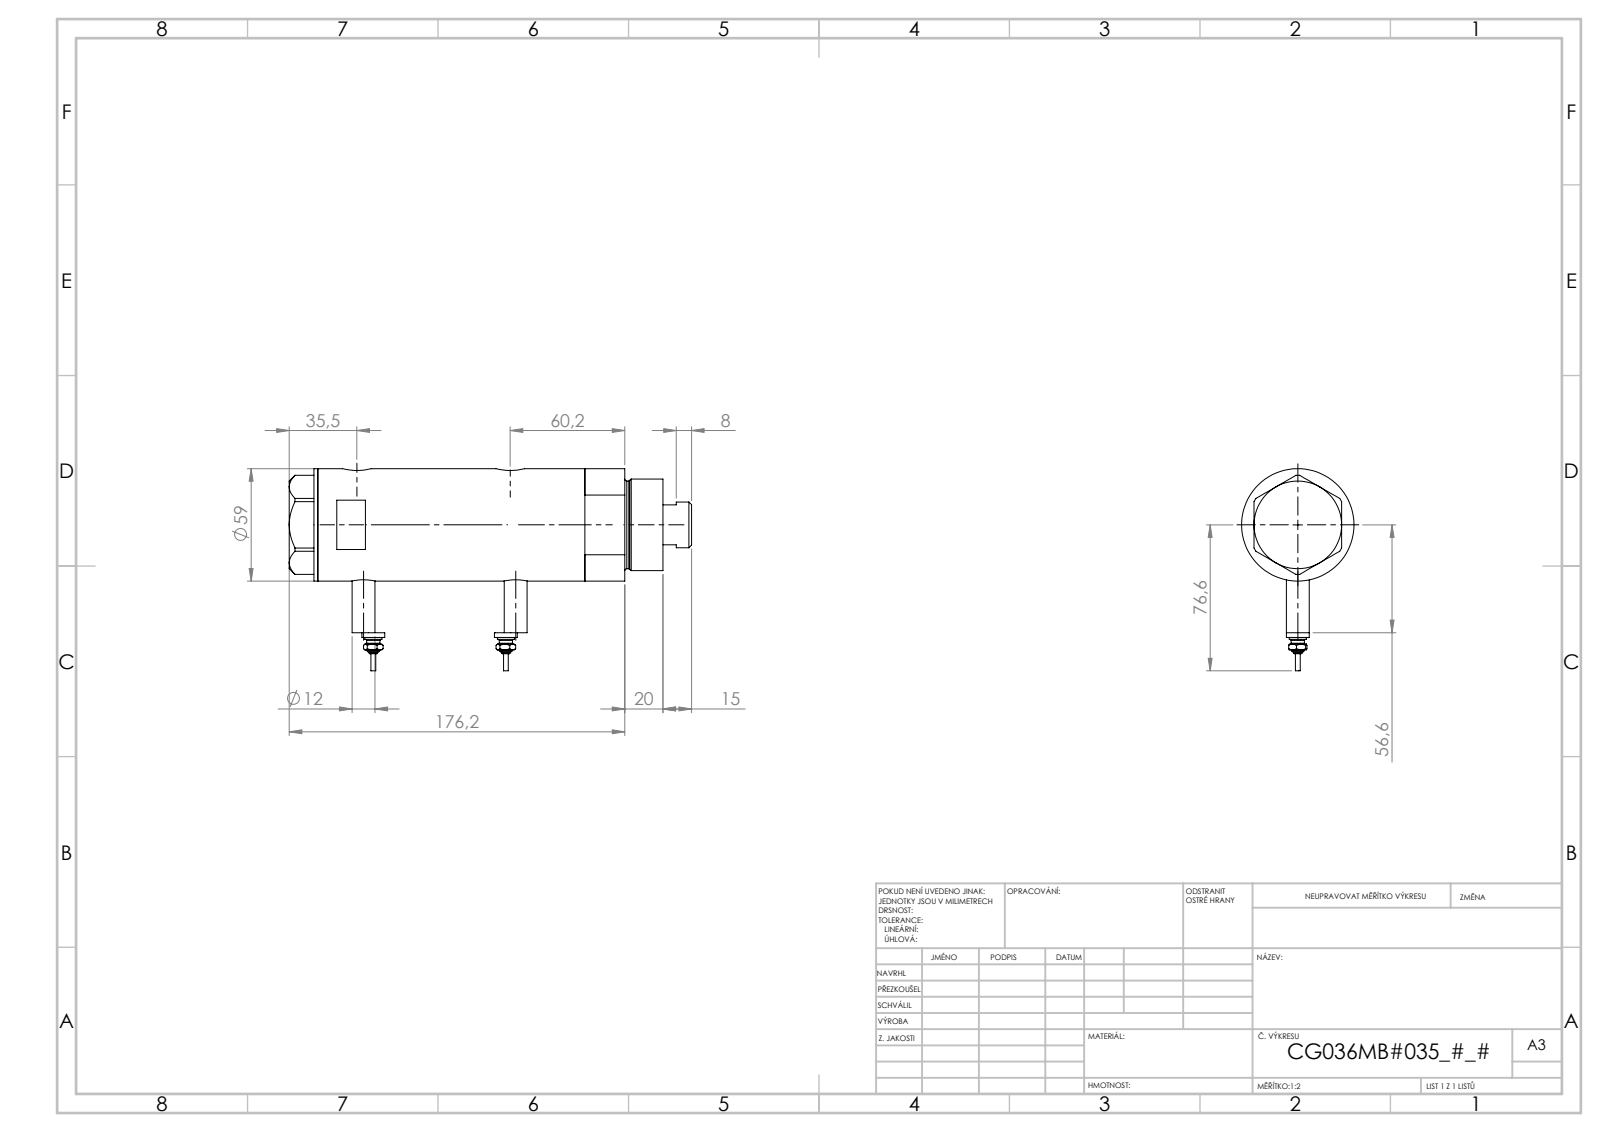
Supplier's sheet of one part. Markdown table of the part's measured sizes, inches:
| quantity | value |
| --- | --- |
| part name | V270CG_BACK; V270CG_FRONT; V270CG_VC; V270CG_MIDDLE (+1 more) |
| STEP written by | SolidWorks 2019 (CONFIG_CONTROL_DESIGN) |
| units | inches |
| bodies | 6 solids, 232 faces (81 planar, 77 cylindrical, 74 other) |
| overall size | 7.812 × 3.594 × 2.323 |
| volume | 27.54 in³ |
| surface area | 150.4 in² |
| round holes (diameter × count) | 0.197 × 2, 0.383 × 2, 0.492 × 2, 0.591 × 2, 0.335 × 1, 0.984 × 1, 1.043 × 1, 1.417 × 1, 1.575 × 1, 2.047 × 1 |
| round bosses / shafts (diameter × count) | 0.472 × 3, 0.354 × 2, 0.276 × 2, 0.171 × 2, 0.094 × 2, 2.323 × 1, 1.89 × 1, 1.811 × 1 |
| main face-to-face distances | 3.635, 0.925, 2.71, 0.591, 1.516, 4.226, 7.221, 6.631, 5.706, 2.995 |
| hole center spacings | 0.114, 0.138, 2.644, 2.758, 2.781, 2.896, 0.114, 0.115 |
